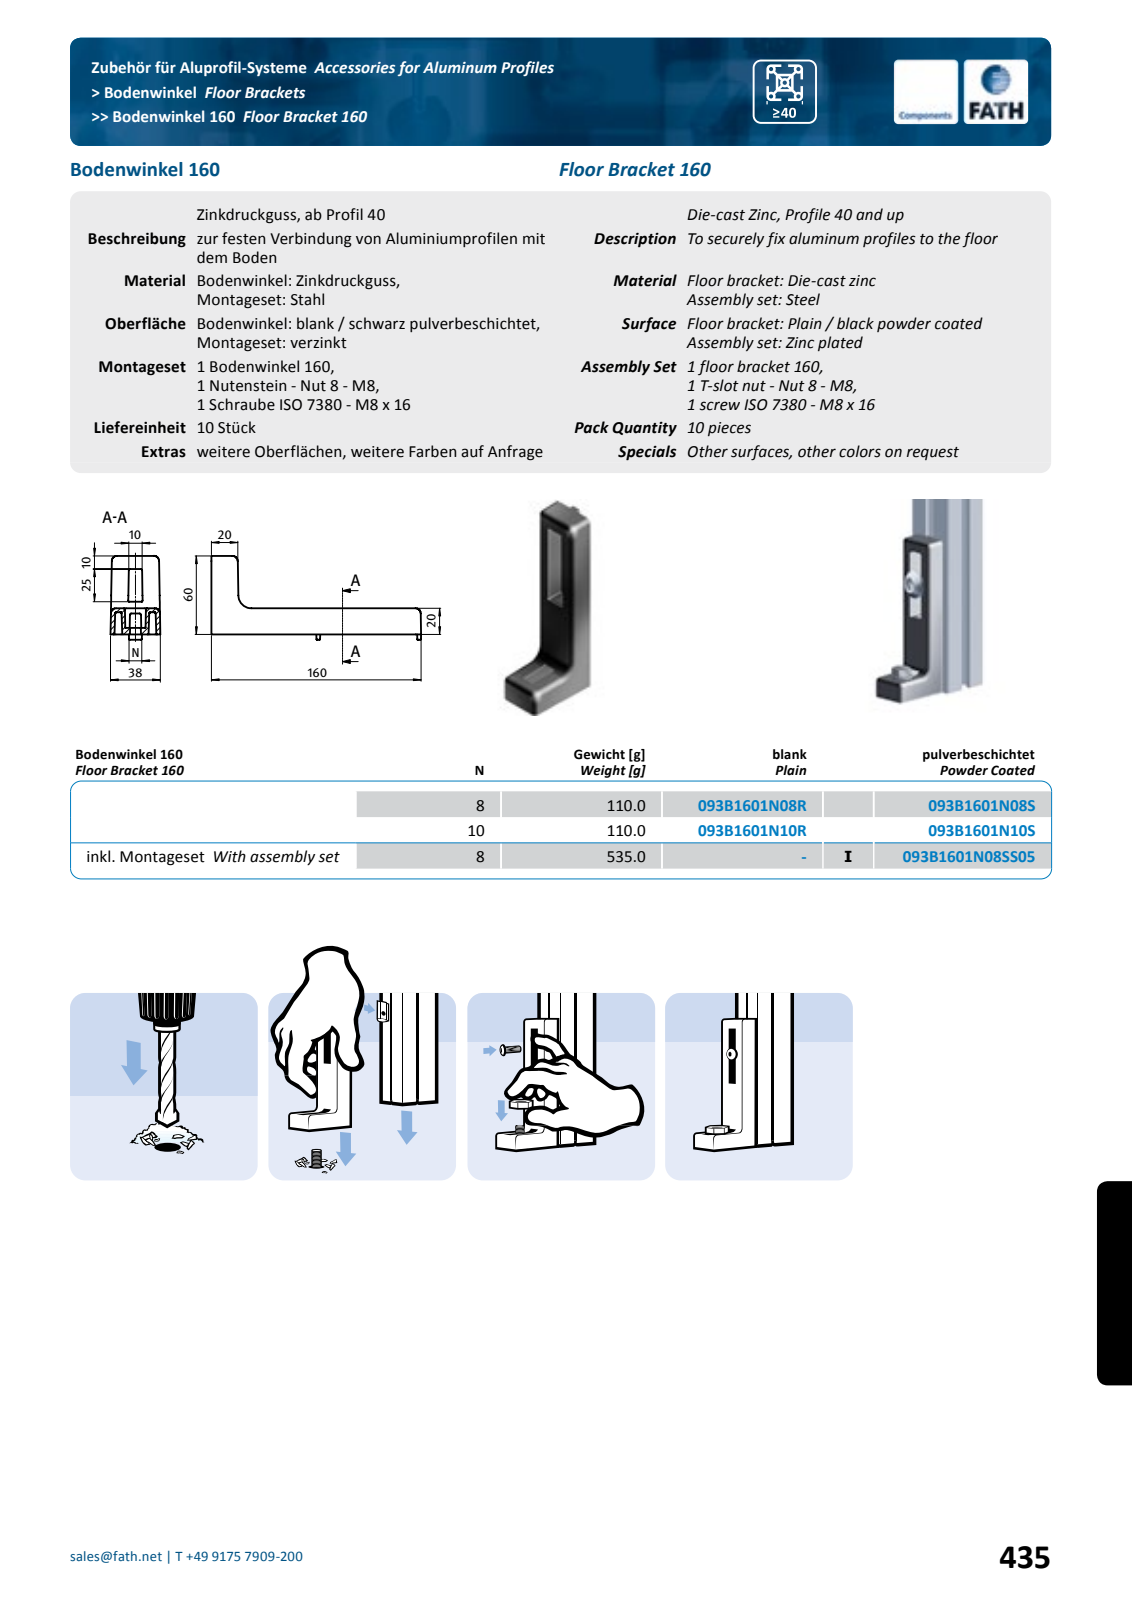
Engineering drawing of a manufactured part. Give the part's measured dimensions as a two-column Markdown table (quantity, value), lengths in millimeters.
| quantity | value |
| --- | --- |
| part name | fath_093b1601n08s |
| STEP written by | Spatial InterOp 3D (automotive_design) |
| units | millimeters |
| bodies | 1 solid, 436 faces (89 planar, 200 cylindrical, 147 other) |
| overall size | 160.01 × 64 × 38 |
| volume | 73 212 mm³ |
| surface area | 41 737 mm² |
| partial cylindrical surfaces (radius × count) | 0.5 × 81, 1 × 66, 4 × 10, 1.5 × 4, 8 × 1, 10 × 1 |
| main face-to-face distances | 20, 10.75, 25.97, 1, 15.91, 26.66, 27, 26.97, 3, 12 |
